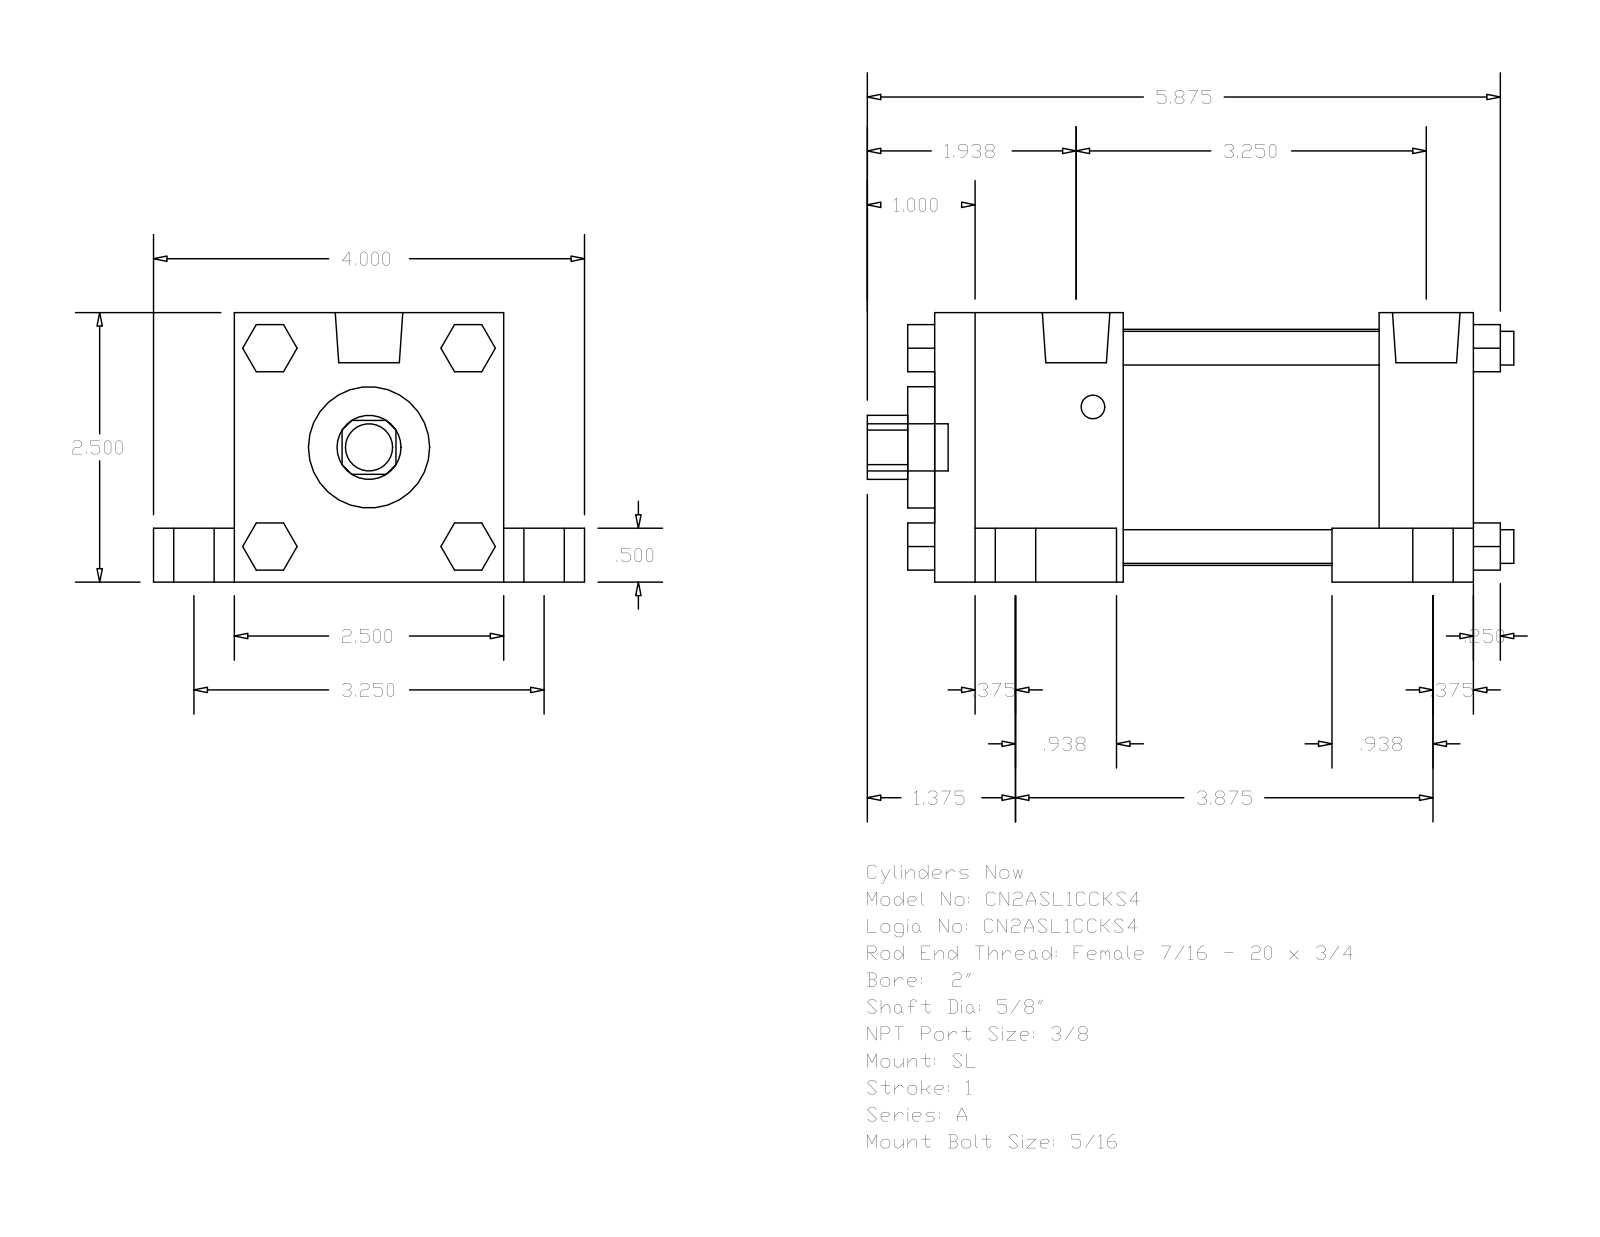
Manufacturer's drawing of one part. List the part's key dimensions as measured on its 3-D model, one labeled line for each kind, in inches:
Part name (STEP PRODUCT): A_SL__0200_0.625
STEP written by: GSSL Pune (CONFIG_CONTROL_DESIGN)
Units: inches
Bodies: 0 solids, 148 faces (112 planar, 36 cylindrical, 0 other)
Overall size (bounding box): 6 × 4 × 2.5
Round holes (diameter × count): ⌀0.625 ×1, ⌀1.125 ×1, ⌀2.19 ×1
Round bosses / shafts (diameter × count): ⌀0.625 ×4, ⌀0.375 ×4, ⌀0.313 ×4, ⌀0.219 ×4, ⌀0.627 ×2, ⌀0.437 ×1
Partial cylindrical surfaces — rounded edges, fillets, slot ends (radius × count): R0.297 ×1
Main face-to-face distances: 2.5, 5, 3.25, 2, 0.5, 0.75, 1.75, 4.125, 2.375, 0.875
